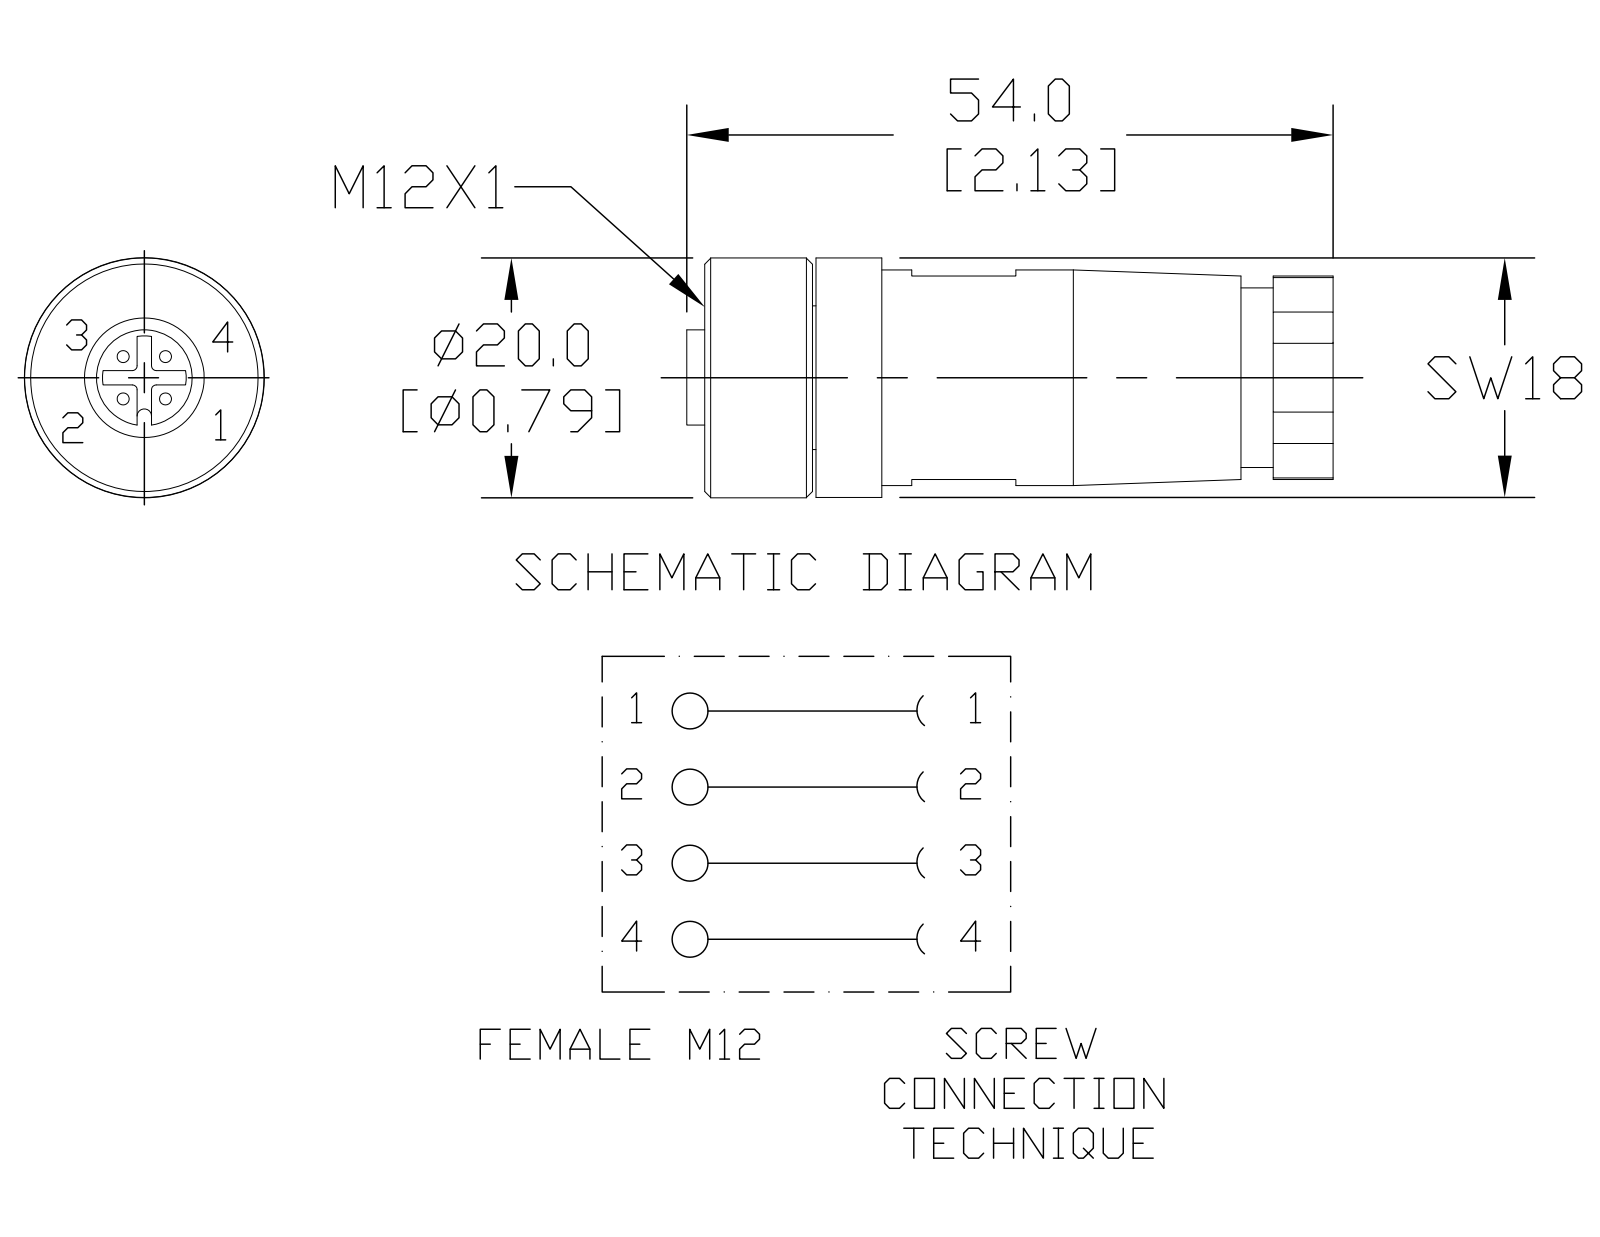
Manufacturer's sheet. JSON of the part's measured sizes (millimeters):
{"part_name": "7000-12941-0000000", "step_written_by": "SolidWorks 2015 (AUTOMOTIVE_DESIGN)", "units": "millimeters", "bodies": {"solids": 1, "faces": 795, "planar": 411, "cylindrical": 202, "other": 182}, "overall_size": [54, 20, 19.99], "volume_mm3": 12246, "surface_area_mm2": 5778, "round_holes": [[1, 5], [9.12, 1], [9.9, 1]], "round_bosses_or_shafts": [[17.78, 1], [11.07, 1], [7.99, 1]], "partial_cylinders_radius": [[10, 1]], "face_to_face_distances": [11.07, 41.93, 53, 16.18, 0.32, 6.02, 35.91, 46.98, 42, 35.98], "hole_center_spacings": [3.3, 3.32, 4.68, 2.22, 2.34, 2.35, 2.46]}
